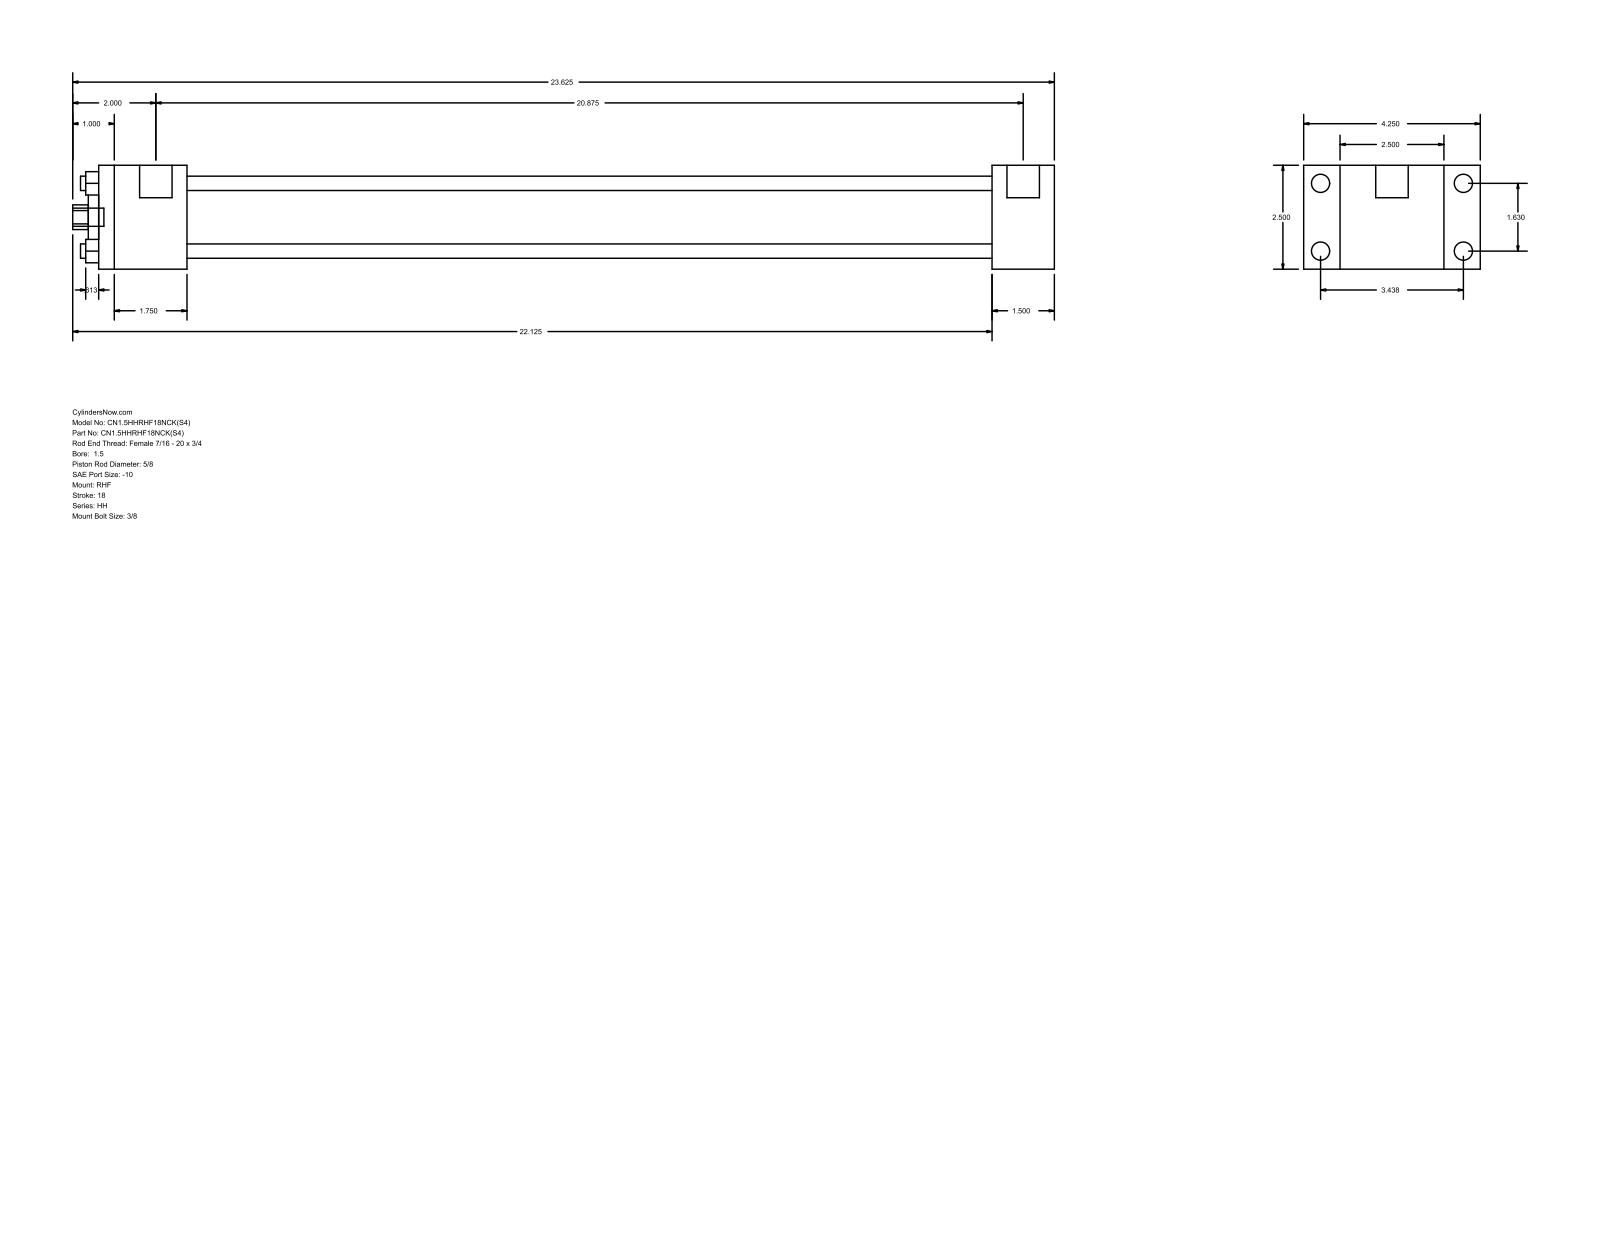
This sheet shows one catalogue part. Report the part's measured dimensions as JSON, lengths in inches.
{"part_name": "HH_RHF__0150_0.625", "step_written_by": "GSSL Pune (CONFIG_CONTROL_DESIGN)", "units": "inches", "bodies": {"solids": 0, "faces": 88, "planar": 60, "cylindrical": 28, "other": 0}, "overall_size": [23.625, 4.25, 2.5], "round_holes": [[0.345, 4], [0.625, 1], [1.125, 1], [1.75, 1]], "round_bosses_or_shafts": [[0.438, 4], [0.219, 4], [0.781, 2], [0.437, 1]], "partial_cylinders_radius": [[0.297, 1]], "face_to_face_distances": [2.5, 1.5, 0.875, 3.375, 21.5, 23, 4.25, 2.125, 19.375, 20.875], "hole_center_spacings": [1.152, 1.63, 2.305]}
